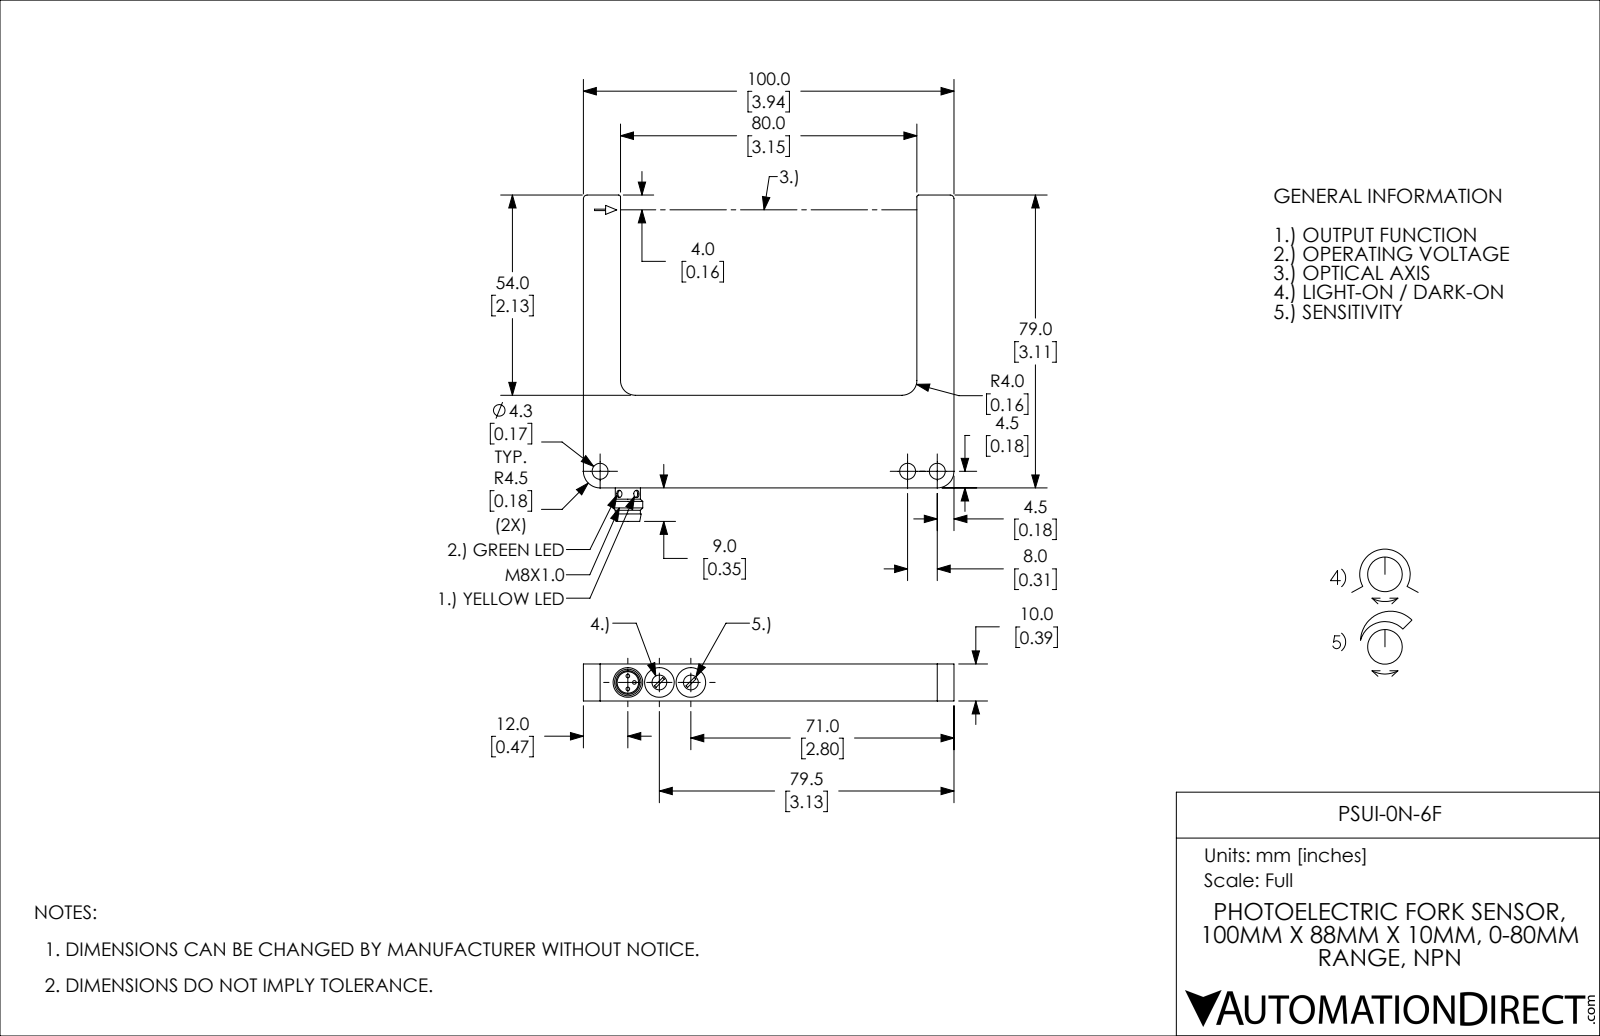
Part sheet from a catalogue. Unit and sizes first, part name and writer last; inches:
Units: inches
Overall size (bounding box): 3.937 × 3.465 × 0.394
Round holes (diameter × count): ⌀0.169 ×3, ⌀0.079 ×2, ⌀0.157 ×2, ⌀0.315 ×2, ⌀0.228 ×1
Round bosses / shafts (diameter × count): ⌀0.039 ×3, ⌀0.315 ×1, ⌀0.267 ×1
Partial cylindrical surfaces — rounded edges, fillets, slot ends (radius × count): R0.02 ×2, R0.039 ×2, R0.063 ×2, R0.157 ×2, R0.177 ×2
Main face-to-face distances: 0.394, 3.543, 3.937, 0.984, 3.15, 2.126, 3.11, 3.106, 0.98, 0.157
Hole centre spacings: 0.335, 0.315, 0.669, 3.268, 3.583
Volume: 2.17 in³ · Surface area: 19.25 in²
Bodies: 1 solid, 71 faces (35 planar, 30 cylindrical, 6 other)
Part name (STEP PRODUCT): PSUI-0N-6F
STEP written by: SolidWorks 2017 (AUTOMOTIVE_DESIGN)
